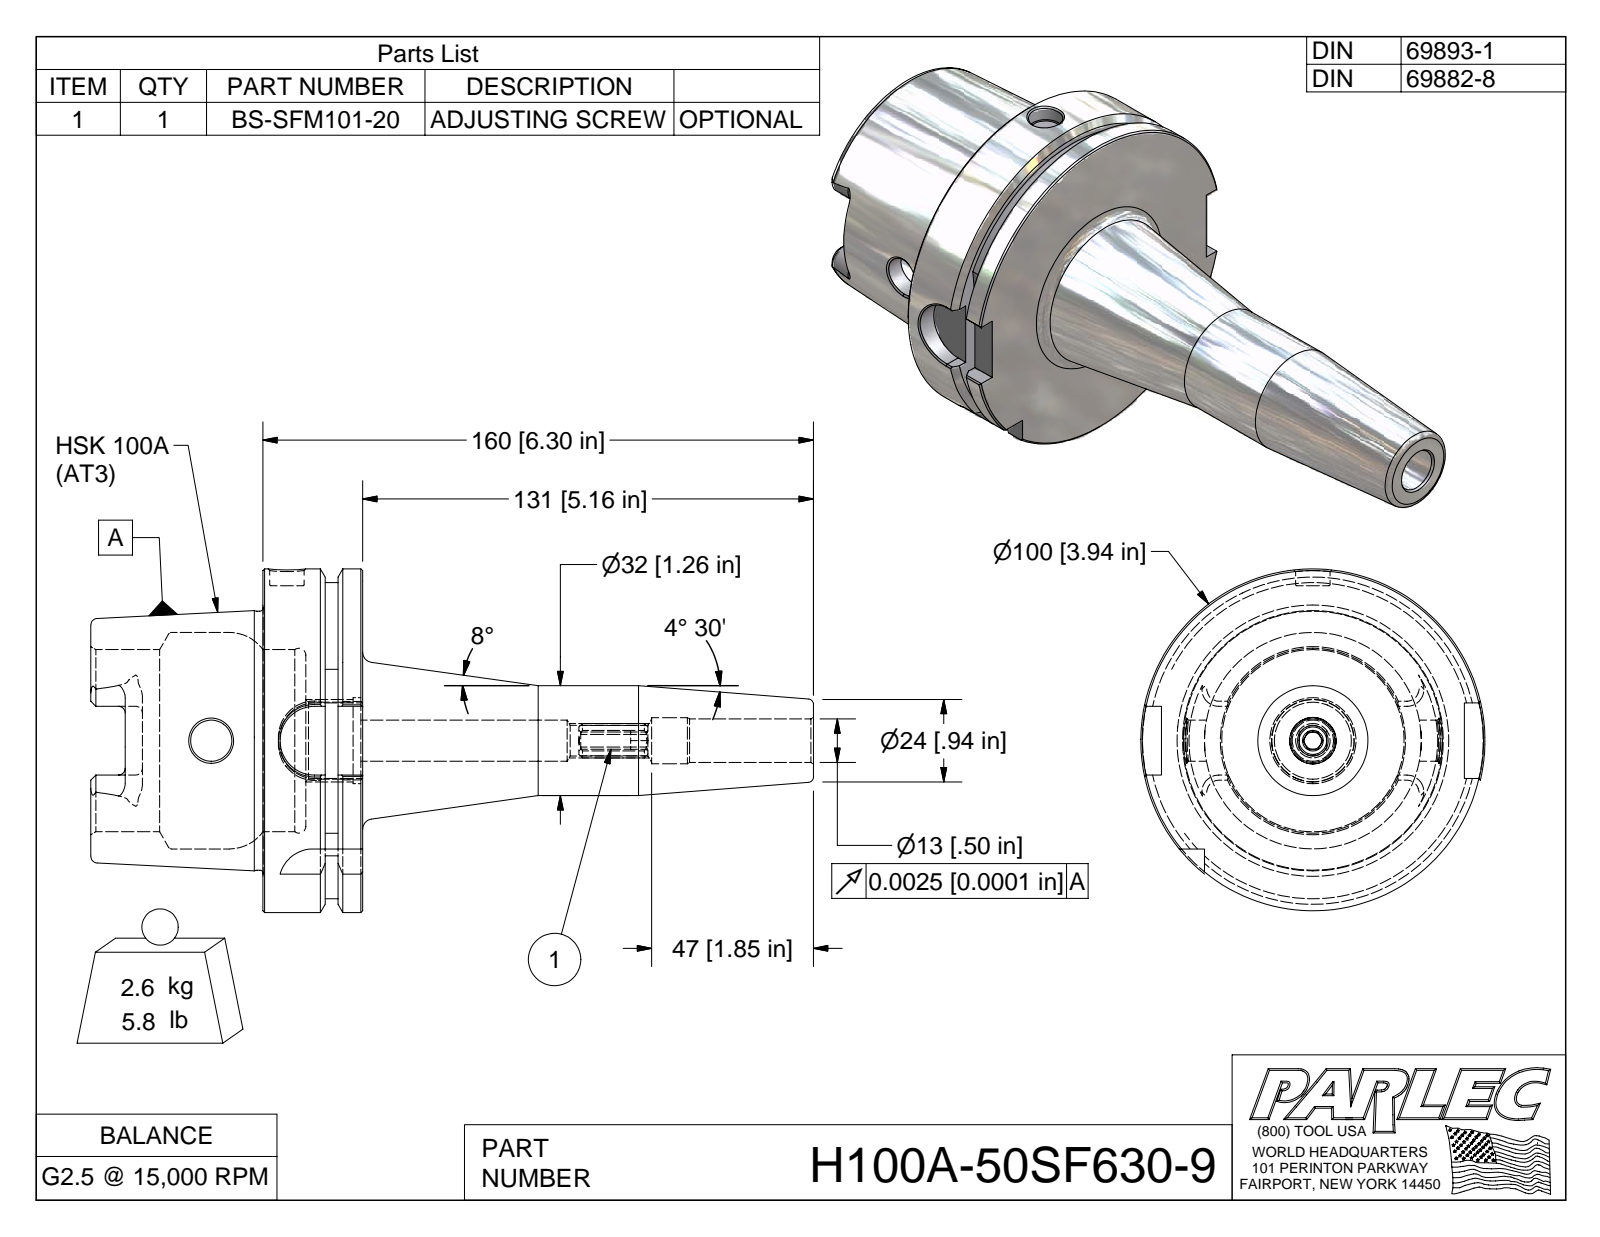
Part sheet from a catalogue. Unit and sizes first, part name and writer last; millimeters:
Units: millimetres
Overall size (bounding box): 210 × 100 × 100
Round holes (diameter × count): ⌀10 ×1, ⌀12 ×1, ⌀12.7 ×1, ⌀13.4 ×1, ⌀22.4 ×1, ⌀25 ×1, ⌀53 ×1, ⌀63 ×1
Round bosses / shafts (diameter × count): ⌀100 ×1, ⌀75.4 ×1, ⌀32 ×1
Partial cylindrical surfaces — rounded edges, fillets, slot ends (radius × count): R10 ×4, R2 ×3, R4.9 ×2, R5 ×1, R46 ×1
Main face-to-face distances: 29, 12.5, 16.5, 50, 62.5, 79, 68.1, 18.1, 5.6, 10.9
Volume: 357 600 mm³ · Surface area: 68 130 mm²
Bodies: 2 solids, 150 faces (49 planar, 30 cylindrical, 71 other)
Part name (STEP PRODUCT): H100A-50SF630-9; H100A-50SF630-9-1; BS-SFM101-20
STEP written by: Autodesk Inventor 2009 (AUTOMOTIVE_DESIGN)
